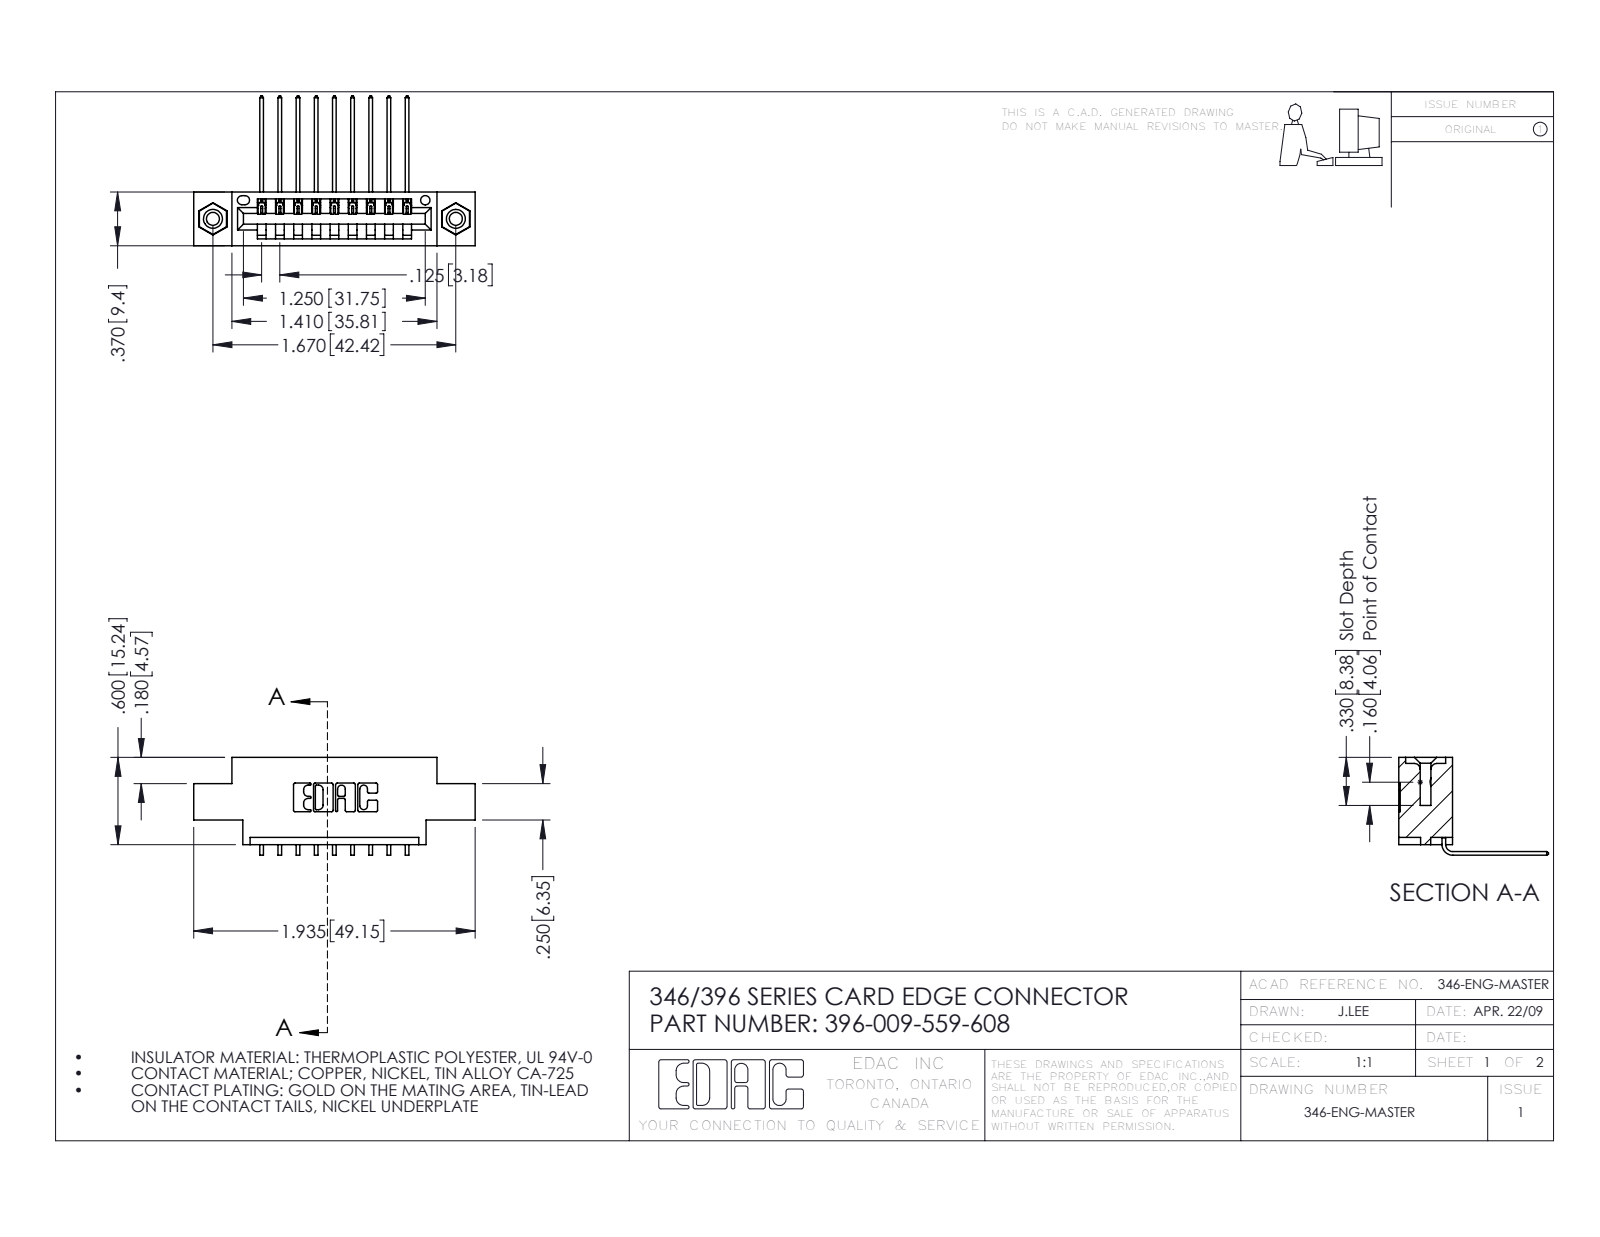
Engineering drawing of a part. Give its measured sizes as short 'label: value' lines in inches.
name: 345-292-001_558 559 Tail - 1; 345-250-001_345-250-003-102; 396-009-559-608; 346 Part_0.170 Offset - 0.156 Dia-TI
written by: SolidWorks 2016 (CONFIG_CONTROL_DESIGN)
unit: in
bodies: 12 solids, 726 faces (490 planar, 220 cylindrical, 16 other)
size: 1.935 × 1.03 × 0.673
volume: 0.265 in³; area: 8.427 in²
holes: 2× ⌀0.089, 2× ⌀0.125, 2× ⌀0.156, 1× ⌀0.064
bosses: 2× ⌀0.155
rounds: 22× R0.01, 18× R0.006, 6× R0.007, 6× R0.031, 3× R0.026, 2× R0.031, 2× R0.04, 1× R0.014
face distances: 0.25, 0.37, 0.048, 0.322, 0.025, 0.072, 0.222, 0.148, 0.1, 0.174
hole spacings: 0.246, 1.465, 1.67
